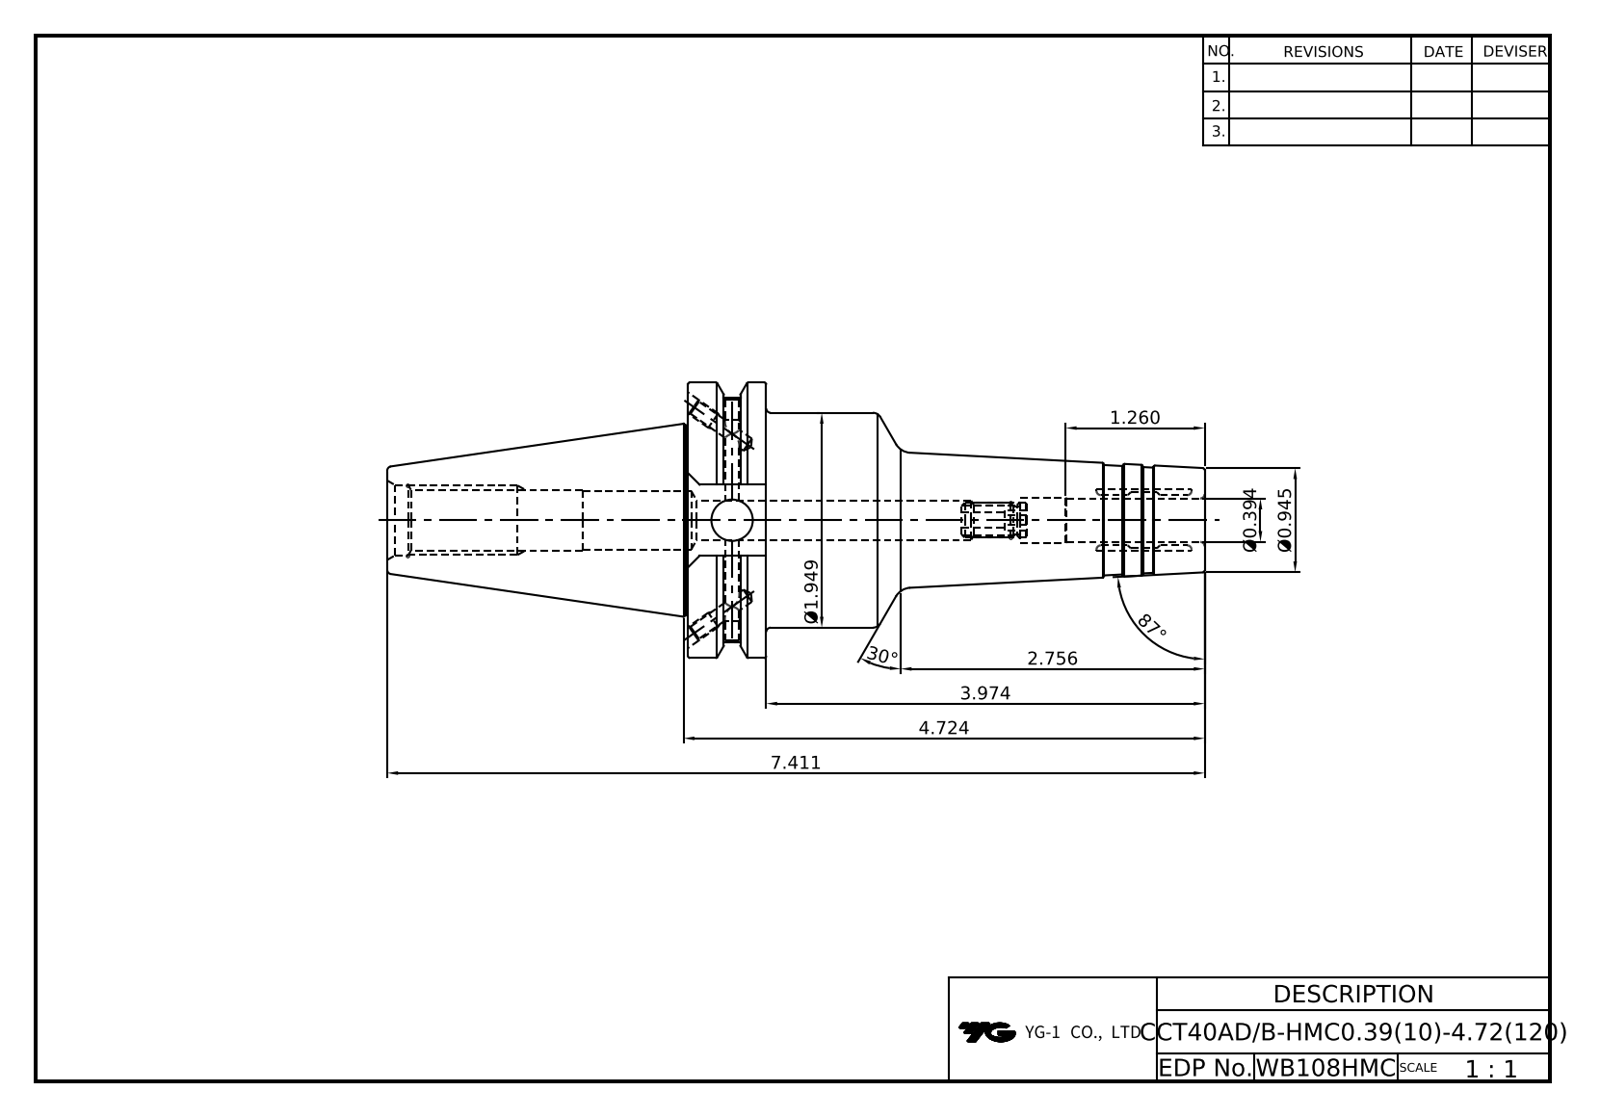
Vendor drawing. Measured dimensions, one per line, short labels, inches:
name: LO-CCT40ADB-HMC10-120
written by: Autodesk Inventor 2022 (AUTOMOTIVE_DESIGN)
unit: in
bodies: 1 solid, 108 faces (35 planar, 31 cylindrical, 42 other)
size: 7.411 × 2.5 × 2.405
volume: 11.98 in³; area: 52.32 in²
holes: 4× ⌀0.128, 2× ⌀0.157, 2× ⌀0.165, 1× ⌀0.272, 1× ⌀0.354, 1× ⌀0.375, 1× ⌀0.394, 1× ⌀0.417, 1× ⌀0.512, 1× ⌀0.527, 1× ⌀0.642
bosses: 1× ⌀2.5, 1× ⌀1.949, 1× ⌀1.724
rounds: 1× R0.322, 1× R1.108
face distances: 0.711, 4.685, 3.974, 1.874, 0.645, 2.726, 3.437, 7.411, 3.202, 0.476
